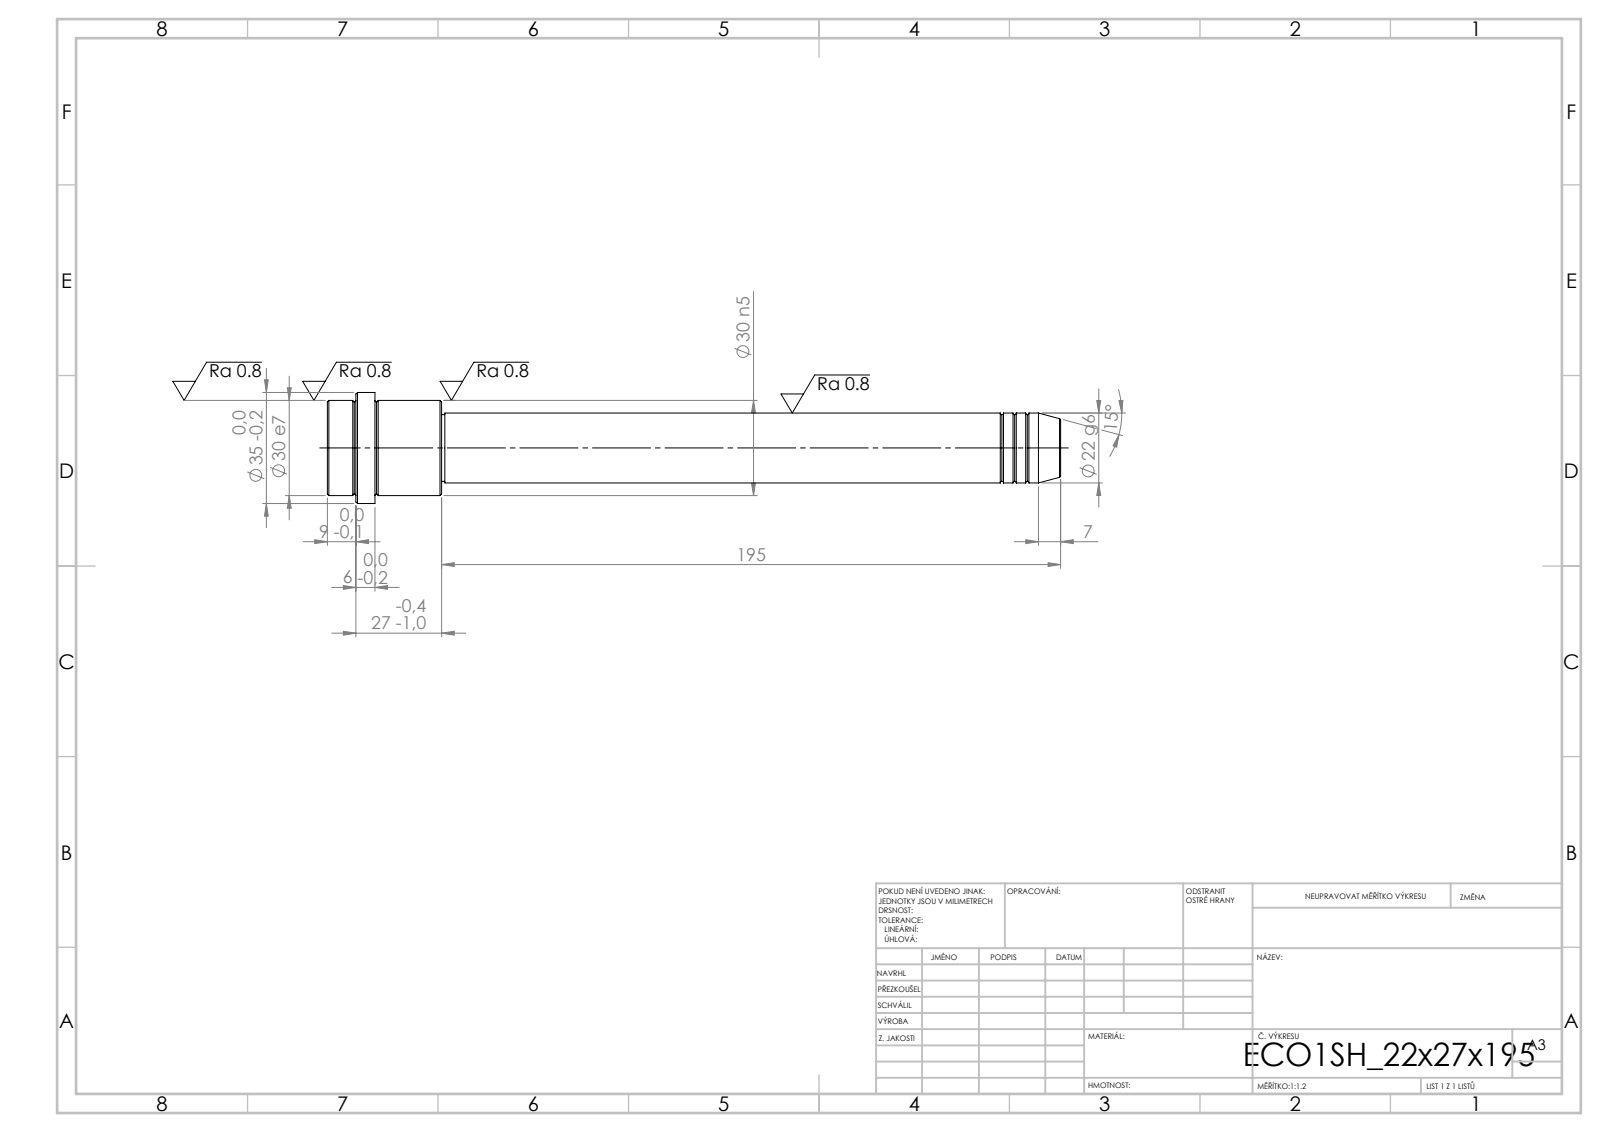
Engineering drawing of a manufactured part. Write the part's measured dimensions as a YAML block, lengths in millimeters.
step_written_by: "SolidWorks 2019 (CONFIG_CONTROL_DESIGN)"
units: millimeters
bodies: {solids: 1, faces: 52, planar: 6, cylindrical: 16, other: 30}
overall_size: [231, 35, 35]
volume: 100451
surface_area: 18924
round_bosses_or_shafts:
  - {diameter: 35, count: 1}
  - {diameter: 30, count: 1}
  - {diameter: 22, count: 1}
  - {diameter: 21, count: 1}
face_to_face_distances: [36, 21, 15, 195, 216, 231, 222, 27, 6, 9]
